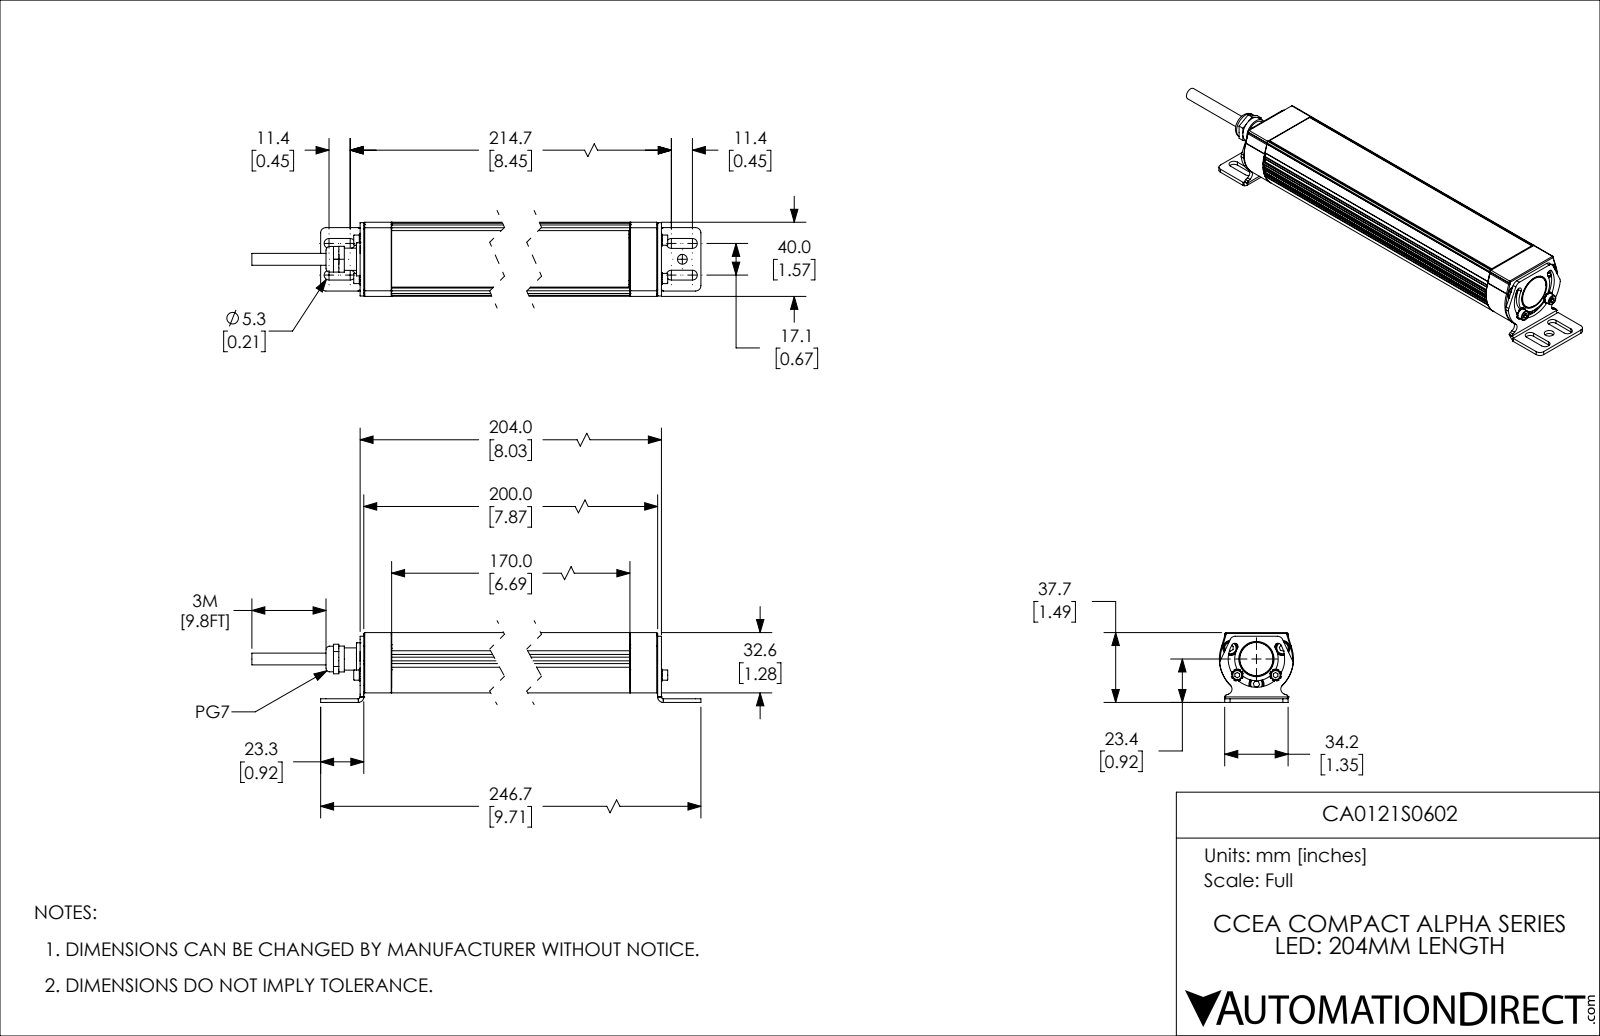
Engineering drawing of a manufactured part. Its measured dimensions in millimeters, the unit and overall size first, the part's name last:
Units: millimetres
Overall size (bounding box): 283.73 × 40 × 37.73
Round holes (diameter × count): ⌀2 ×4, ⌀3.3 ×3, ⌀4.5 ×3, ⌀7.5 ×3, ⌀2.5 ×2, ⌀3.2 ×2, ⌀5.3 ×2, ⌀8.5 ×1, ⌀11.5 ×1, ⌀12 ×1, ⌀14 ×1, ⌀19 ×1
Round bosses / shafts (diameter × count): ⌀1 ×4, ⌀7 ×3, ⌀4 ×3, ⌀5.5 ×2, ⌀3 ×2, ⌀18.3 ×1, ⌀15 ×1, ⌀13.86 ×1
Partial cylindrical surfaces — rounded edges, fillets, slot ends (radius × count): R0.25 ×56, R1 ×22, R3 ×22, R2.65 ×8, R2.85 ×6, R5.5 ×6, R1.5 ×4, R0.3 ×2
Main face-to-face distances: 2, 4, 28.49, 32.49, 28.48, 4.01, 1.5, 0.5, 202, 11.51
Hole centre spacings: 13.5, 1, 4.68, 5.63, 11.41, 13.07, 13.16, 15.09
Volume: 116 115 mm³ · Surface area: 87 970 mm²
Bodies: 22 solids, 1181 faces (391 planar, 577 cylindrical, 213 other)
Part name (STEP PRODUCT): CA0121S0602
STEP written by: SolidWorks 2021 (CONFIG_CONTROL_DESIGN)
